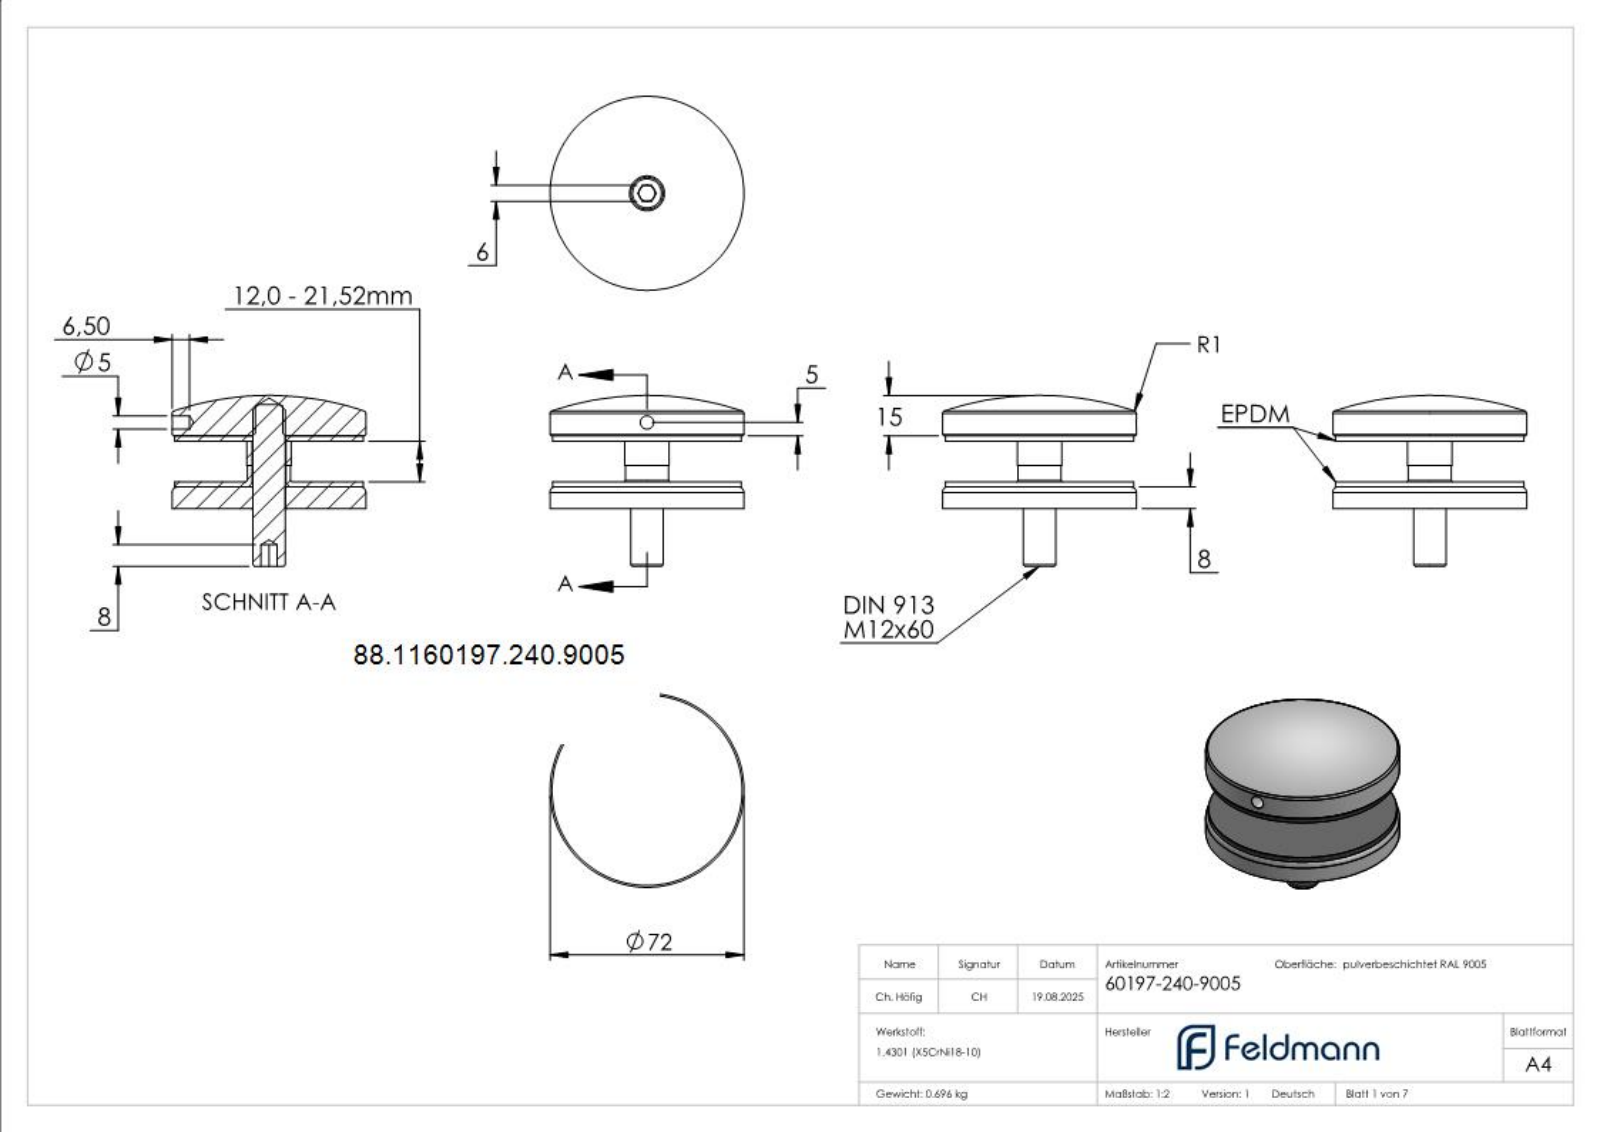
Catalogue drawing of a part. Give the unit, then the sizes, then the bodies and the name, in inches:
Units: inches
Overall size (bounding box): 2.835 × 2.835 × 2.495
Round holes (diameter × count): ⌀0.197 ×1, ⌀0.402 ×1, ⌀0.472 ×1, ⌀0.492 ×1
Round bosses / shafts (diameter × count): ⌀2.835 ×1, ⌀2.756 ×1, ⌀0.65 ×1, ⌀0.63 ×1
Main face-to-face distances: 0.079, 0.669, 0.748, 0.315, 1.063, 0.984, 0.394, 0.591, 0.236, 0.63
Volume: 6.217 in³ · Surface area: 62.78 in²
Bodies: 6 solids, 317 faces (165 planar, 13 cylindrical, 139 other)
Part name (STEP PRODUCT): 60197-XXX Teil3_60197-XXX Teil3; 60197-XXX Teil1_60197-240-9005 Teil1; 60197-XXX Teil4_60197-XXX Teil4; 60197-240-9005 (+3 more)
STEP written by: SolidWorks 2018 (CONFIG_CONTROL_DESIGN)
